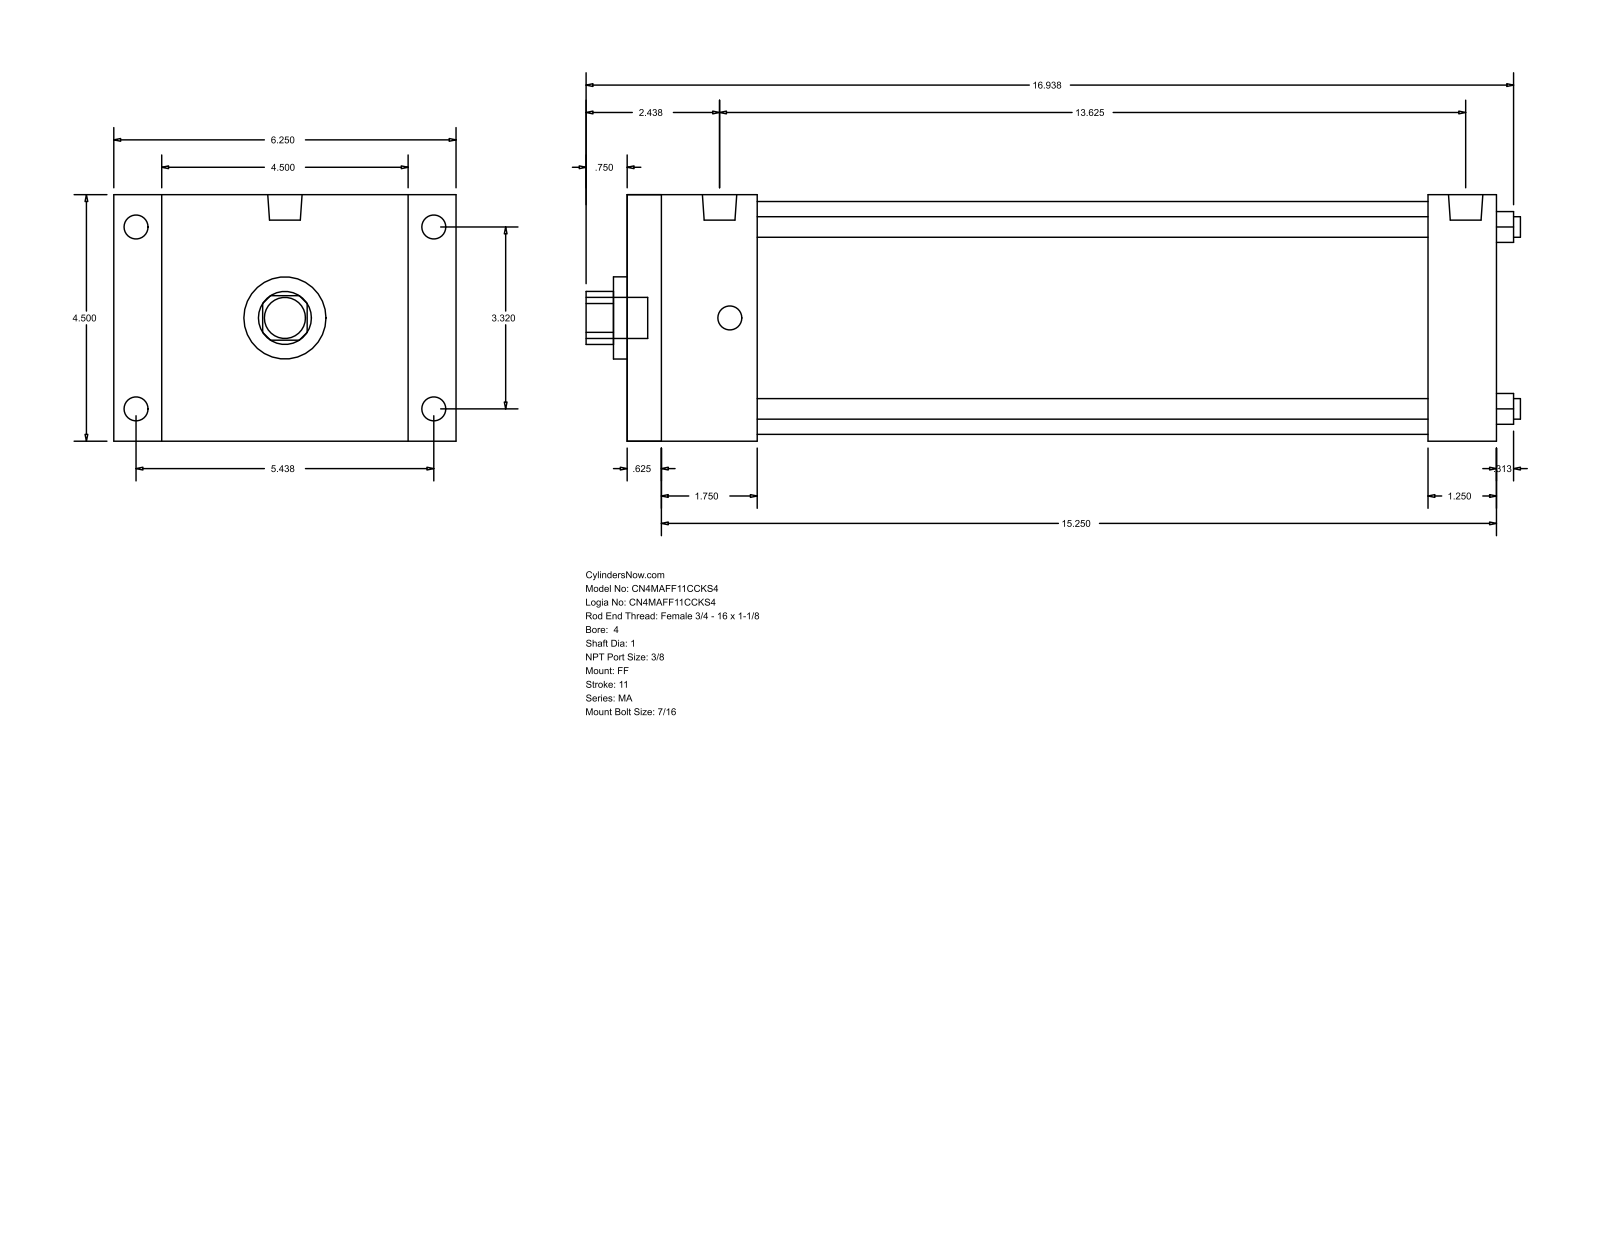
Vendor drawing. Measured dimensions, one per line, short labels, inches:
name: MA_FF__0400_1
written by: GSSL Pune (CONFIG_CONTROL_DESIGN)
unit: in
bodies: 0 solids, 92 faces (64 planar, 28 cylindrical, 0 other)
size: 17.063 × 6.25 × 4.5
holes: 4× ⌀0.375, 1× ⌀1, 1× ⌀1.5, 1× ⌀4.25
bosses: 8× ⌀0.437, 2× ⌀0.627, 1× ⌀0.75
rounds: 1× R0.484
face distances: 4.5, 15.875, 0.625, 15.25, 0.875, 5.375, 14.625, 14, 1.25, 2.375
hole spacings: 2.347, 3.32, 4.695
